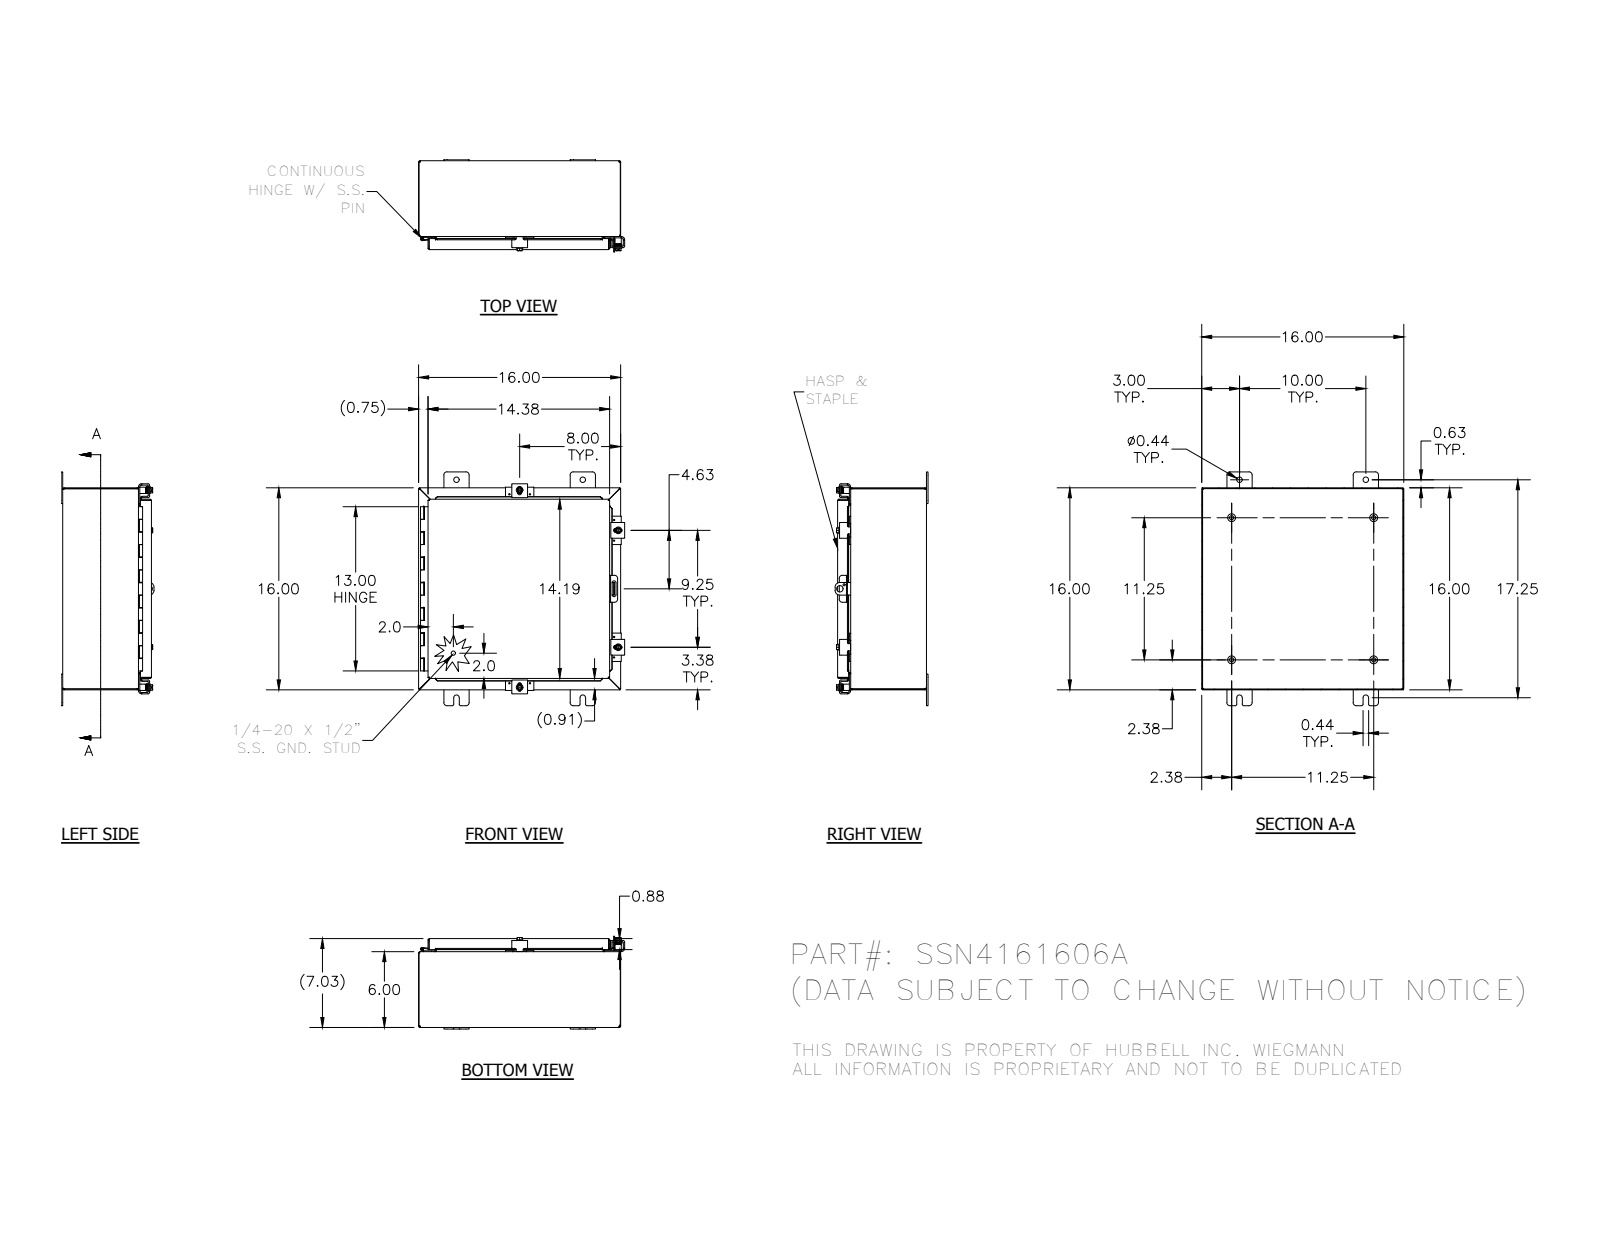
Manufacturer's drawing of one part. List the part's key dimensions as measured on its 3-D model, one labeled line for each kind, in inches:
Part name (STEP PRODUCT): 32874-16T; SSN4161606ABKP; 30818; 30824-2 (+8 more)
STEP written by: SolidWorks 2014 (AUTOMOTIVE_DESIGN)
Units: inches
Bodies: 37 solids, 1384 faces (551 planar, 592 cylindrical, 241 other)
Overall size (bounding box): 18.5 × 16.216 × 7.355
Volume: 88.01 in³ · Surface area: 2 283 in²
Round holes (diameter × count): ⌀0.11 ×8, ⌀0.211 ×4, ⌀0.281 ×4, ⌀0.3 ×4, ⌀0.438 ×4, ⌀0.125 ×1, ⌀0.156 ×1, ⌀0.5 ×1
Round bosses / shafts (diameter × count): ⌀0.25 ×6, ⌀0.625 ×4, ⌀0.52 ×4, ⌀0.5 ×4, ⌀0.35 ×4, ⌀0.33 ×4, ⌀0.337 ×1, ⌀0.12 ×1
Partial cylindrical surfaces — rounded edges, fillets, slot ends (radius × count): R0.03 ×49, R0.125 ×33, R0.25 ×29, R0.031 ×23, R0.105 ×23, R0.062 ×14, R0.07 ×8, R0.141 ×8
Main face-to-face distances: 0.074, 6.959, 15.926, 6.885, 7.033, 16, 15.852, 5.926, 1.033, 6
Hole centre spacings: 0.876, 15.311, 9.25, 0.876, 1.625, 1.625, 4.189, 4.341
